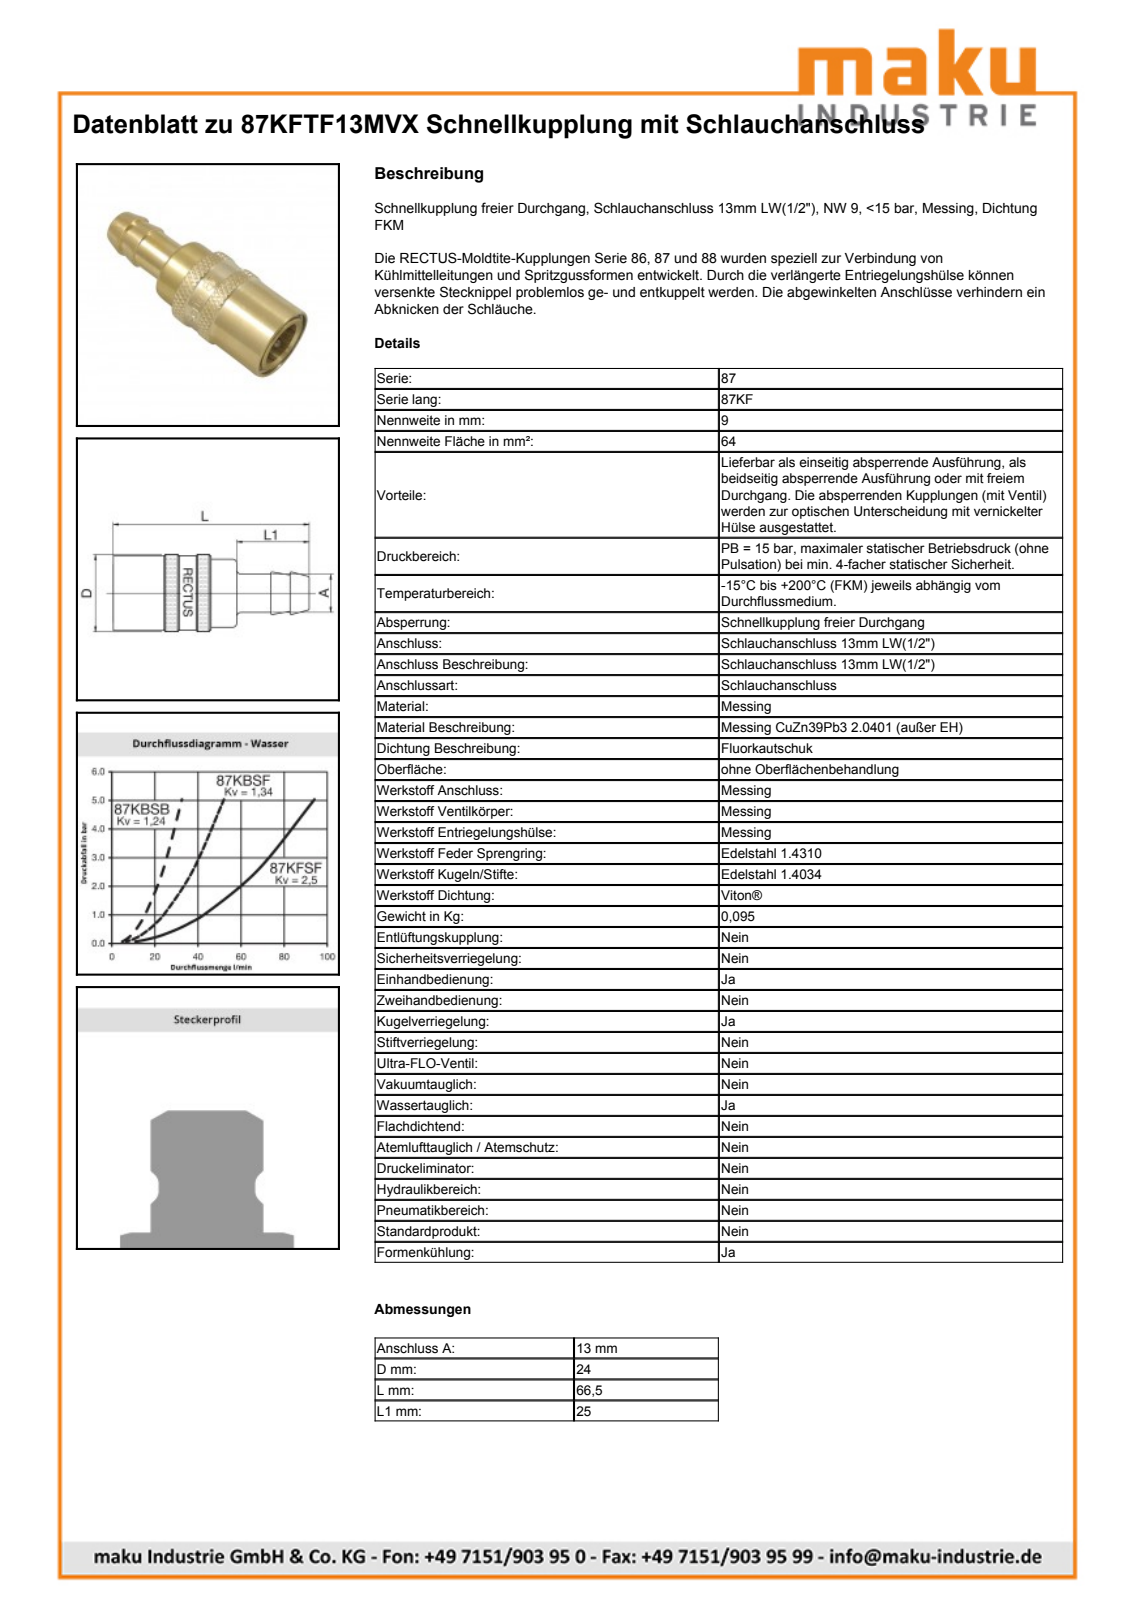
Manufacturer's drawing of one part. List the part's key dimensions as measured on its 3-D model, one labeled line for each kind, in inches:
Part name (STEP PRODUCT): D108545
STEP written by: Autodesk Inventor 2013 (AUTOMOTIVE_DESIGN)
Units: inches
Bodies: 2 solids, 448 faces (140 planar, 58 cylindrical, 250 other)
Overall size (bounding box): 2.62 × 0.951 × 0.951
Volume: 1.117 in³ · Surface area: 14.61 in²
Round holes (diameter × count): ⌀0.689 ×1, ⌀0.738 ×1, ⌀0.829 ×1, ⌀0.837 ×1
Round bosses / shafts (diameter × count): ⌀0.951 ×1, ⌀0.906 ×1, ⌀0.807 ×1, ⌀0.709 ×1, ⌀0.679 ×1, ⌀0.648 ×1, ⌀0.5 ×1
Partial cylindrical surfaces — rounded edges, fillets, slot ends (radius × count): R0.315 ×1, R0.449 ×1
Main face-to-face distances: 0.447, 2.173, 2.62, 1.772, 0.402, 0.848, 0.984, 0.787, 1.189, 1.636
